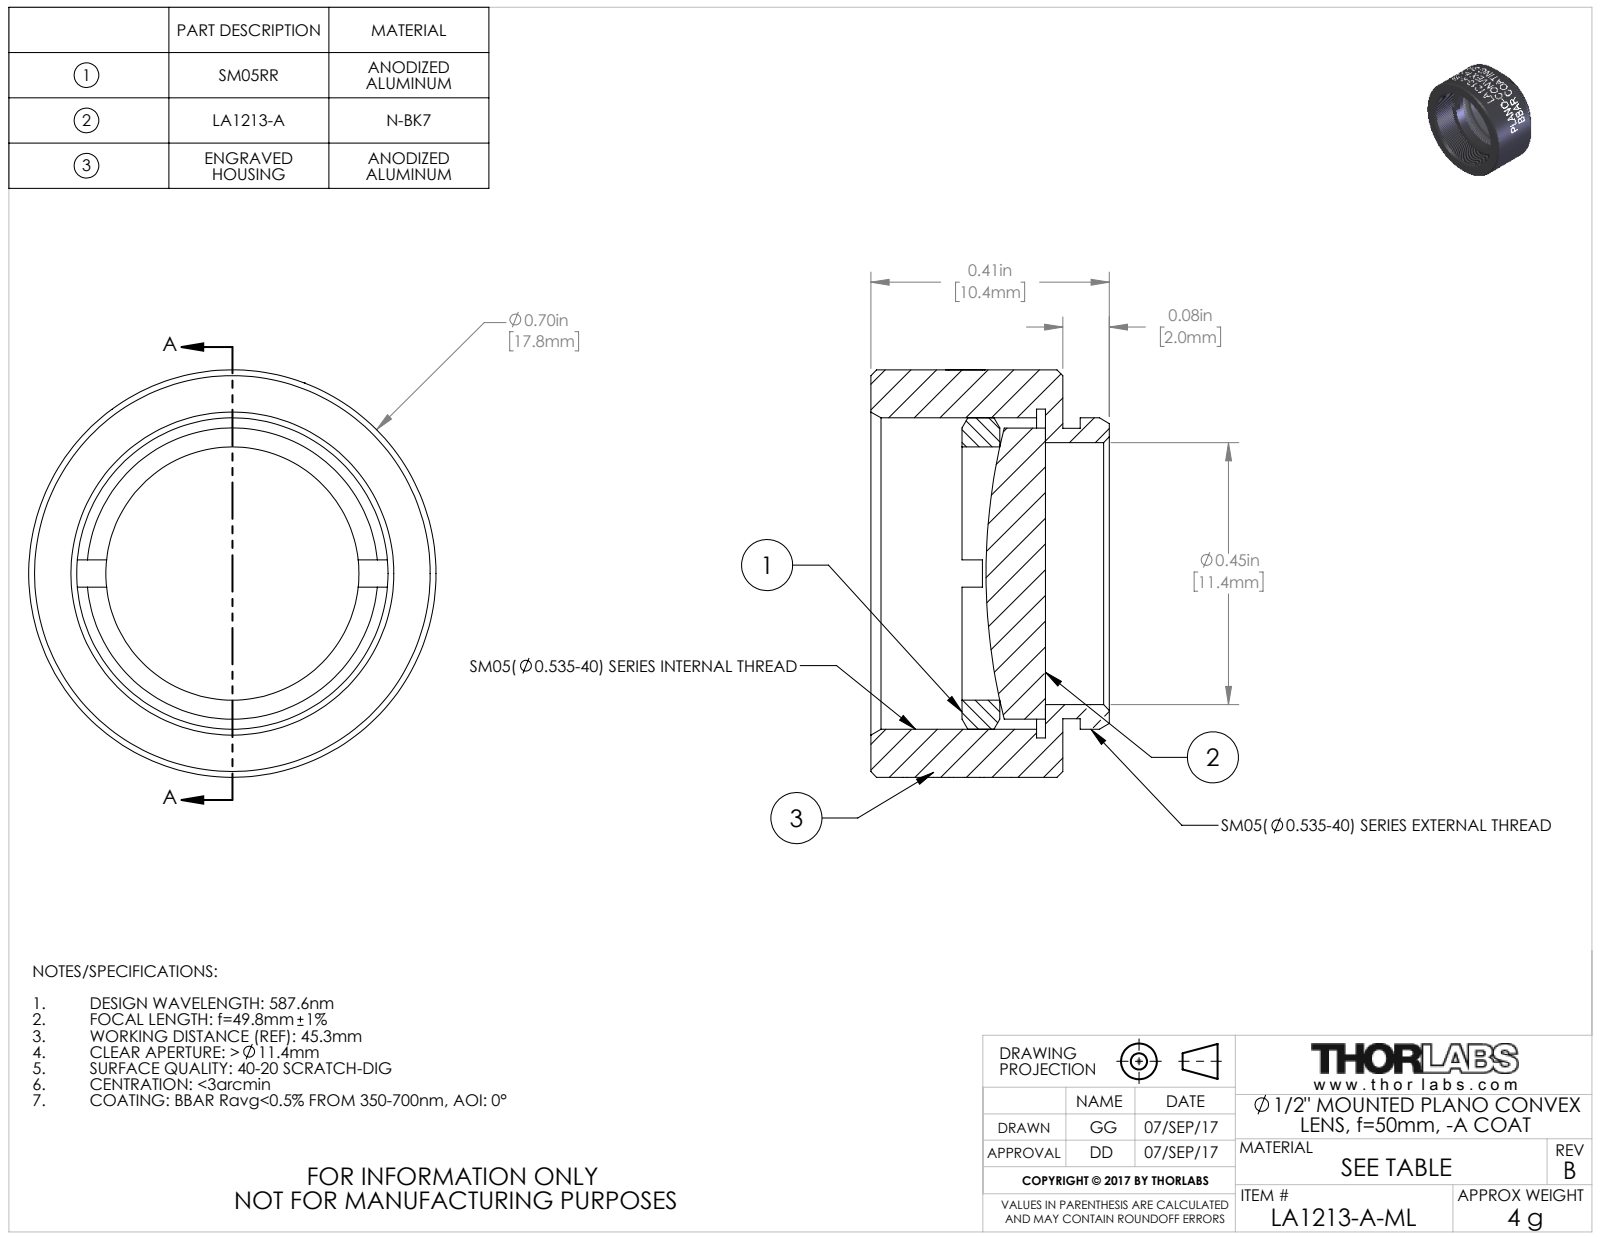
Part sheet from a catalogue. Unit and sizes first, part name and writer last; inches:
Units: inches
Overall size (bounding box): 0.7 × 0.7 × 0.41
Round holes (diameter × count): ⌀0.435 ×1, ⌀0.45 ×1, ⌀0.535 ×1, ⌀0.565 ×1
Round bosses / shafts (diameter × count): ⌀0.7 ×1, ⌀0.535 ×1, ⌀0.5 ×1, ⌀0.499 ×1
Partial cylindrical surfaces — rounded edges, fillets, slot ends (radius × count): R0.35 ×1
Main face-to-face distances: 0.03, 0.3, 0.33, 0.109, 0.078, 0.222, 0.174, 0.143, 0.065, 0.157
Volume: 0.08 in³ · Surface area: 2.855 in²
Bodies: 3 solids, 274 faces (94 planar, 105 cylindrical, 75 other)
Part name (STEP PRODUCT): 24399-E0W
STEP written by: SolidWorks 2016 (CONFIG_CONTROL_DESIGN)
